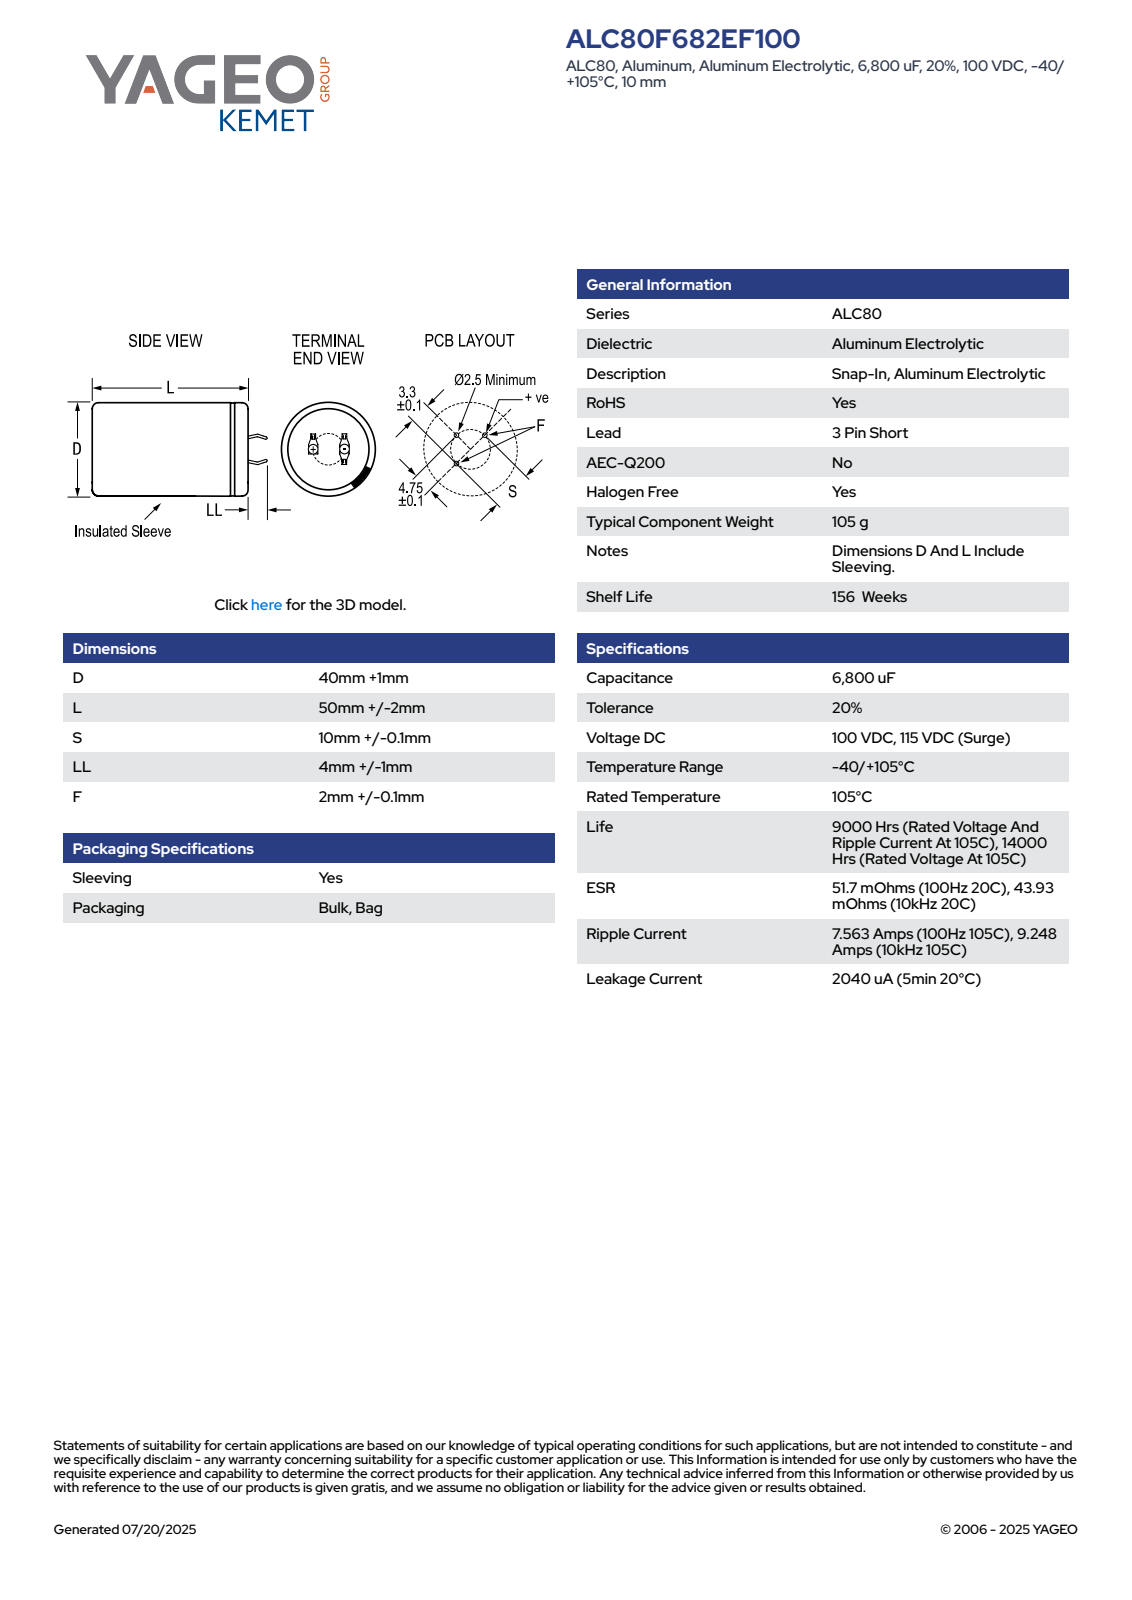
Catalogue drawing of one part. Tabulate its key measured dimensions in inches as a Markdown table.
| quantity | value |
| --- | --- |
| part name | CARS_K3P_40X50_D41L52S10LL5F2.1 |
| STEP written by | SolidWorks 2014 (AUTOMOTIVE_DESIGN) |
| units | inches |
| bodies | 1 solid, 115 faces (61 planar, 15 cylindrical, 39 other) |
| overall size | 2.244 × 1.614 × 1.614 |
| volume | 4.142 in³ |
| surface area | 14.45 in² |
| round holes (diameter × count) | 1.428 × 1 |
| round bosses / shafts (diameter × count) | 1.614 × 1 |
| partial cylindrical surfaces (radius × count) | 0.807 × 1 |
| main face-to-face distances | 2.047, 2.067, 0.02, 0.024, 0.324, 0.03, 0.053, 0.023, 0.023, 0.294 |
